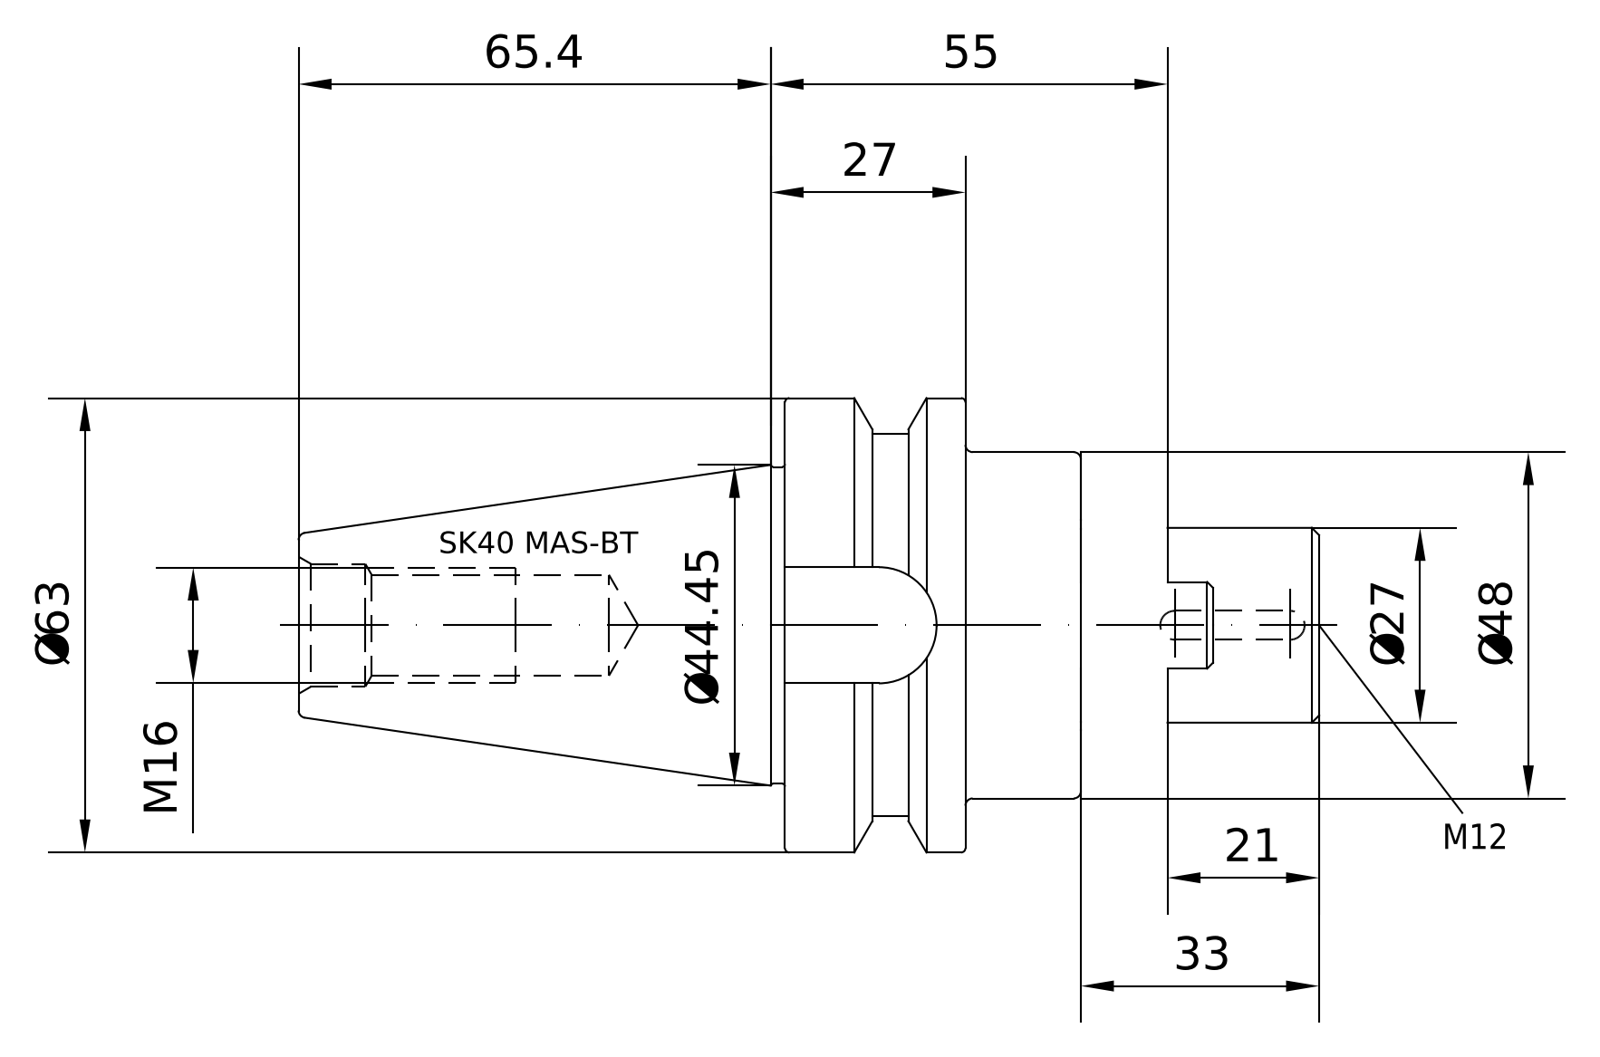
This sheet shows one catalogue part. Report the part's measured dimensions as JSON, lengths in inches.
{"part_name": "40-540-27; 85-200-27; 40-540-27_ASM", "step_written_by": "PRO/ENGINEER BY PARAMETRIC TECHNOLOGY CORPORATION, 2010430 (CONFIG_CONTROL_DESIGN)", "units": "inches", "bodies": {"solids": 2, "faces": 188, "planar": 92, "cylindrical": 38, "other": 58}, "overall_size": [5.567, 2.48, 2.48], "volume_in3": 11.17, "surface_area_in2": 56.14, "round_holes": [[0.402, 1], [0.472, 1], [0.545, 1], [0.67, 1], [0.689, 1], [1.077, 1], [1.24, 1]], "round_bosses_or_shafts": [[2.48, 1], [2.077, 1], [1.89, 1], [1.722, 1], [1.063, 1], [0.63, 1]], "partial_cylinders_radius": [[0.138, 2], [0.238, 1], [0.319, 1]], "face_to_face_distances": [1.614, 0.984, 0.63, 2.087, 1.102, 0.472, 2.913, 1.929, 1.299, 0.827]}
